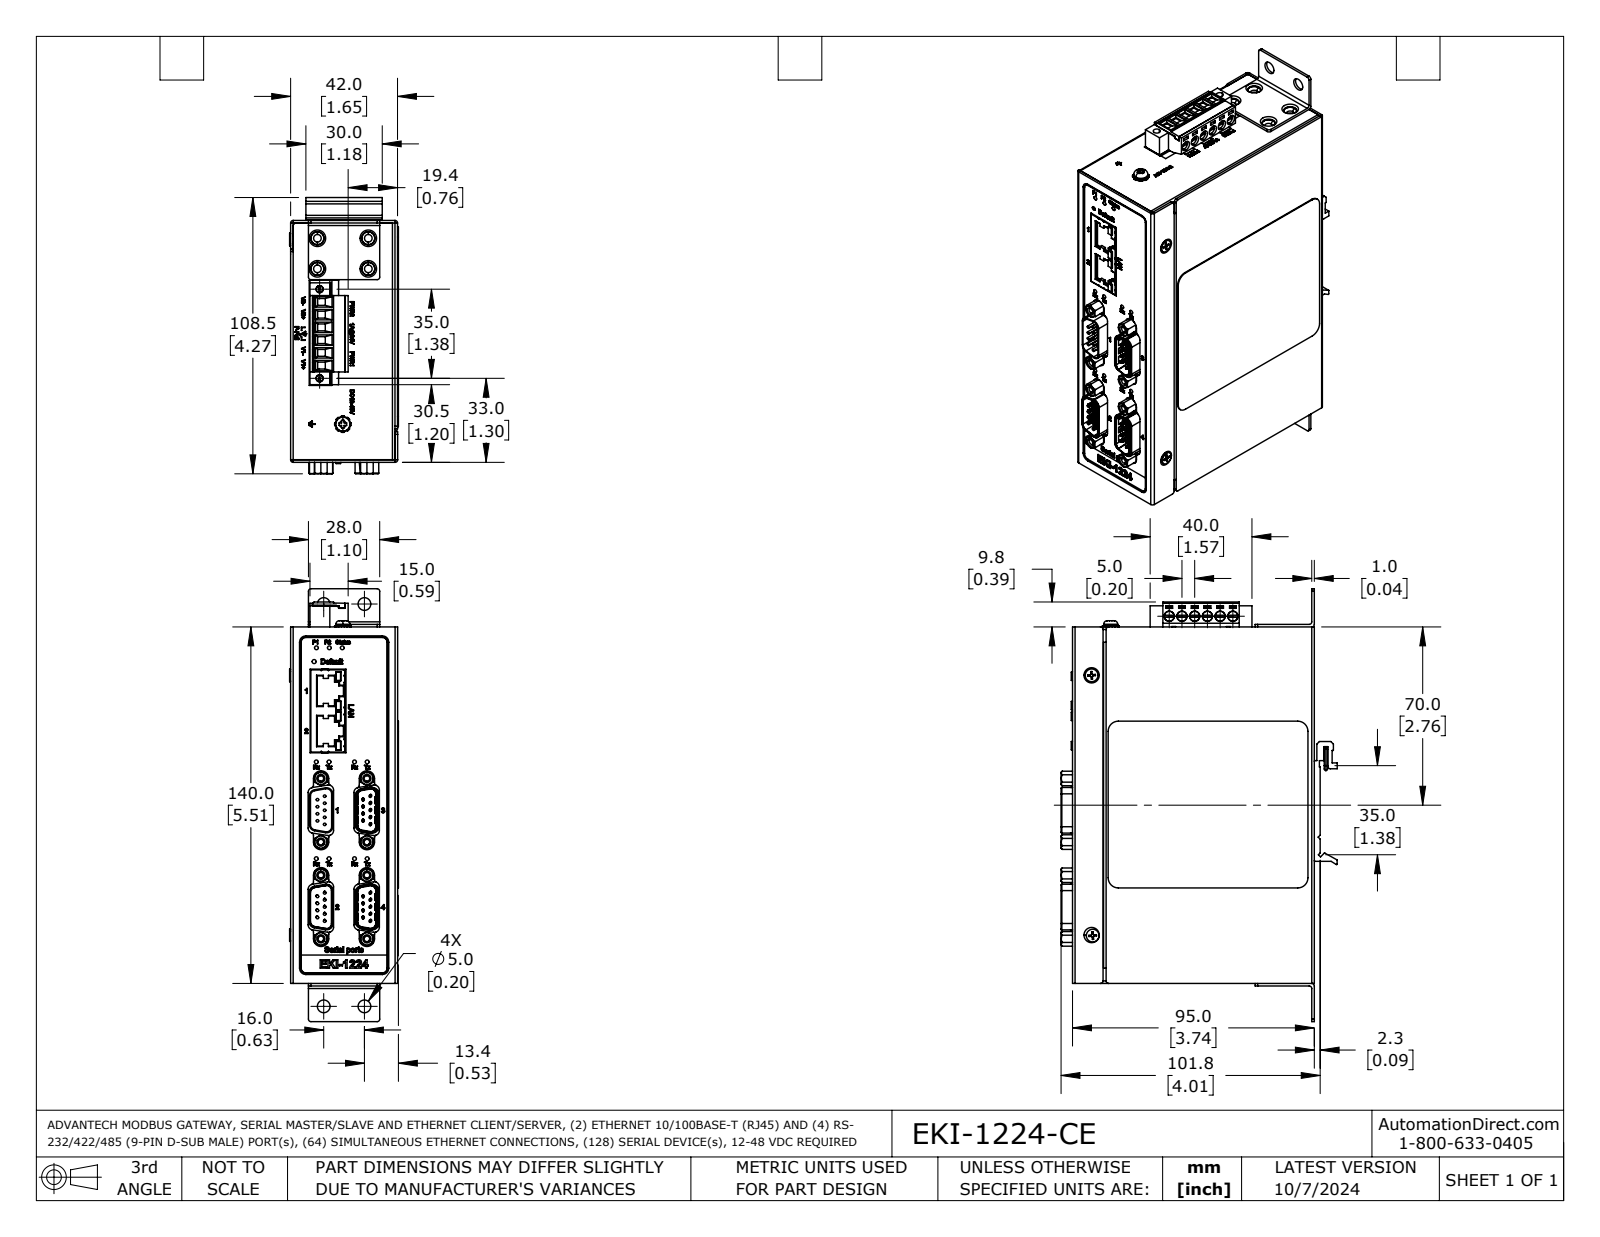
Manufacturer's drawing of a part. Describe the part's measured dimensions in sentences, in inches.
The part is named "EKI-1224-CE". Its 3-D file was written by "SolidWorks 2021 (AUTOMOTIVE_DESIGN)". It is 18 solids with 3447 faces: 1882 planar, 834 cylindrical and 731 other. Overall it measures 6.693 by 4.272 by 1.683 inches. Its volume is 30.94 cubic inches and its surface area 195.5 square inches. Round holes: 23 of diameter 0.138, 11 of diameter 0.059, 8 of diameter 0.087, 6 of diameter 0.094, 6 of diameter 0.157, 4 of diameter 0.118, 4 of diameter 0.197, 4 of diameter 0.201, 2 of diameter 0.079, 2 of diameter 0.11, 1 of diameter 0.063, 1 of diameter 0.098. Round bosses or shafts: 18 of diameter 0.039, 18 of diameter 0.031, 10 of diameter 0.197, 8 of diameter 0.112, 6 of diameter 0.154, 6 of diameter 0.118, 6 of diameter 0.051, 2 of diameter 0.106. Partial cylindrical surfaces (rounded edges, fillets, slot ends): 53 of radius 0.039, 38 of radius 0.012, 36 of radius 0.079, 32 of radius 0.014, 23 of radius 0.02, 17 of radius 0.016, 14 of radius 0.004, 12 of radius 0.098. The main face-to-face distances are 0.039, 1.614, 1.654, 0.014, 0.041, 3.72, 3.681, 0.48, 0.52, 3.201. The hole center spacings are 1.496, 0.197, 0.591, 0.984, 0.984, 0.394, 0.713, 0.787.
